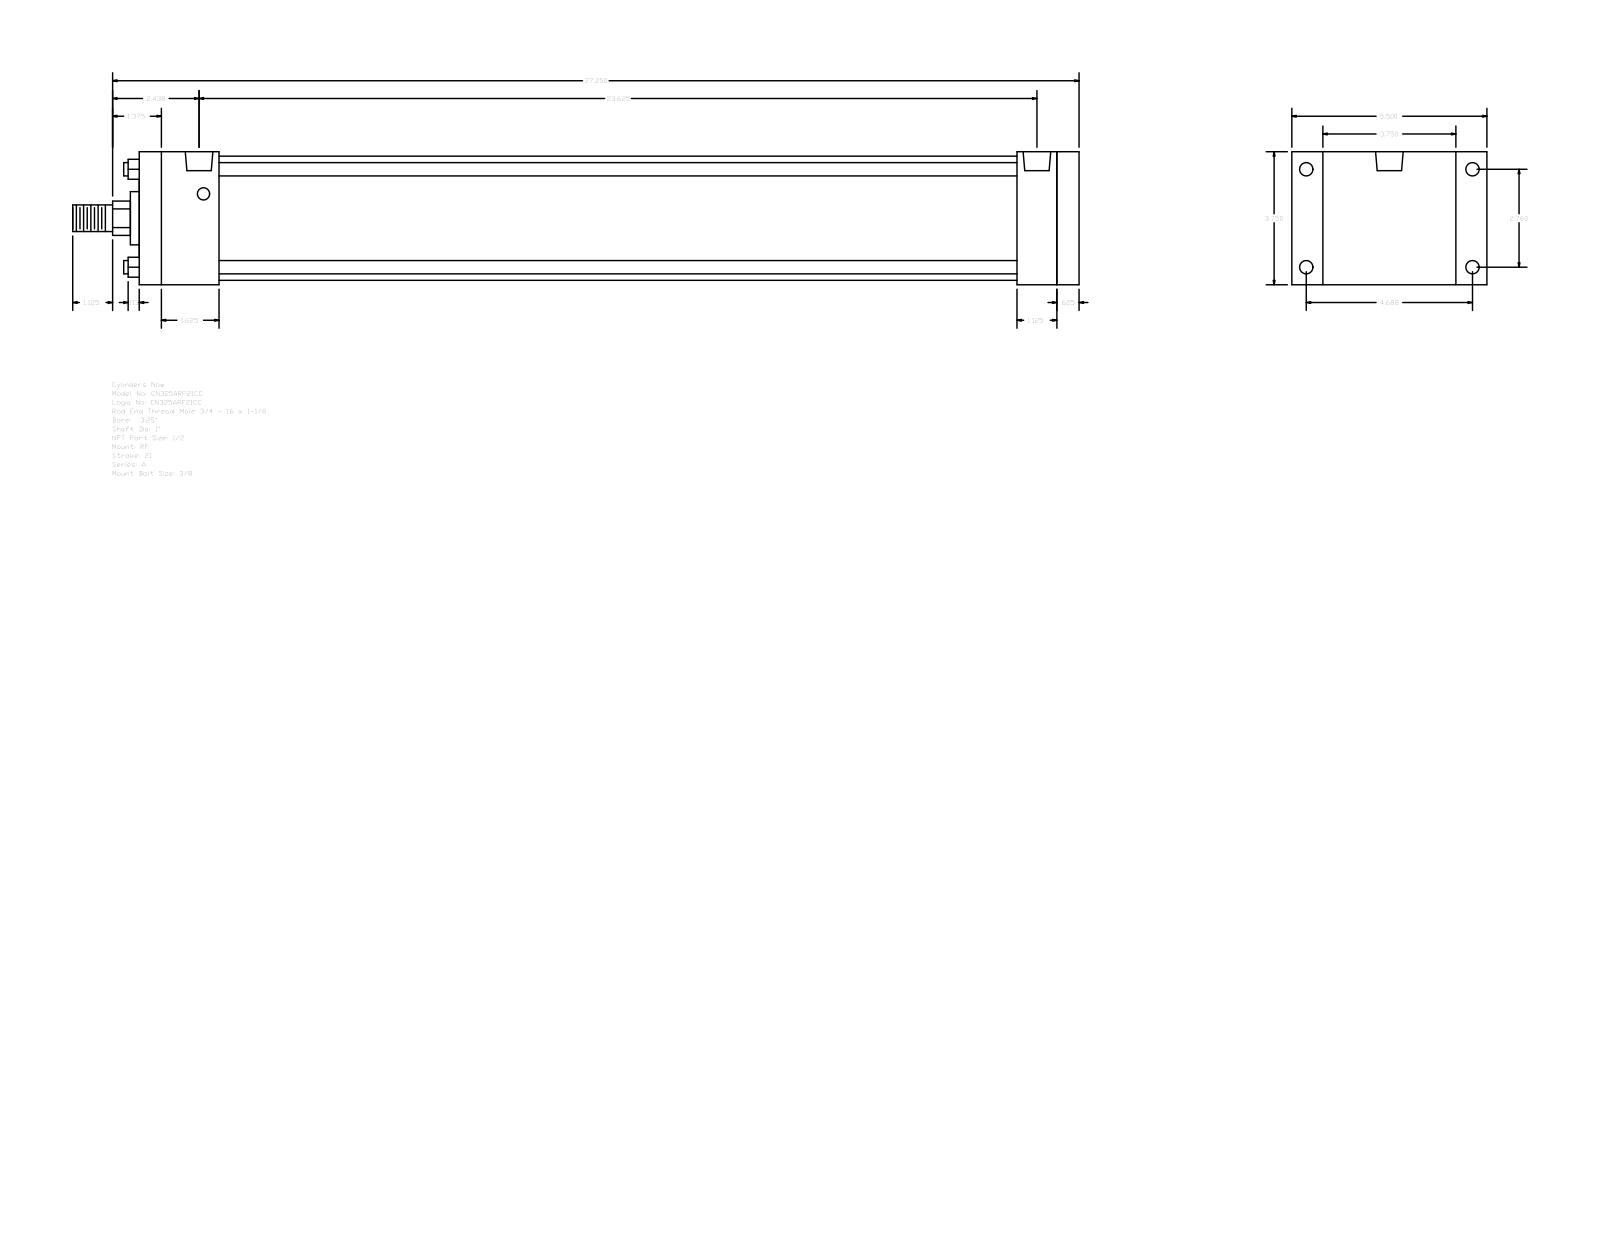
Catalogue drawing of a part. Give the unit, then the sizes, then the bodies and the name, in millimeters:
Units: millimetres
Overall size (bounding box): 720.73 × 139.7 × 95.25
Round holes (diameter × count): ⌀8.73 ×4, ⌀9.53 ×4, ⌀19.77 ×2
Round bosses / shafts (diameter × count): ⌀9.53 ×4, ⌀88.9 ×1, ⌀38.1 ×1, ⌀25.4 ×1, ⌀19.05 ×1
Partial cylindrical surfaces — rounded edges, fillets, slot ends (radius × count): R12.29 ×1
Main face-to-face distances: 95.24, 673.1, 657.22, 15.88, 22.23, 117.47, 28.57, 628.65, 44.45, 57.15
Hole centre spacings: 3.18, 70.1, 119.06, 138.16, 593.72, 596.9, 600.08
Bodies: 0 solids, 92 faces (64 planar, 28 cylindrical, 0 other)
Part name (STEP PRODUCT): A_RF__0325_1
STEP written by: GSSL Pune (CONFIG_CONTROL_DESIGN)
